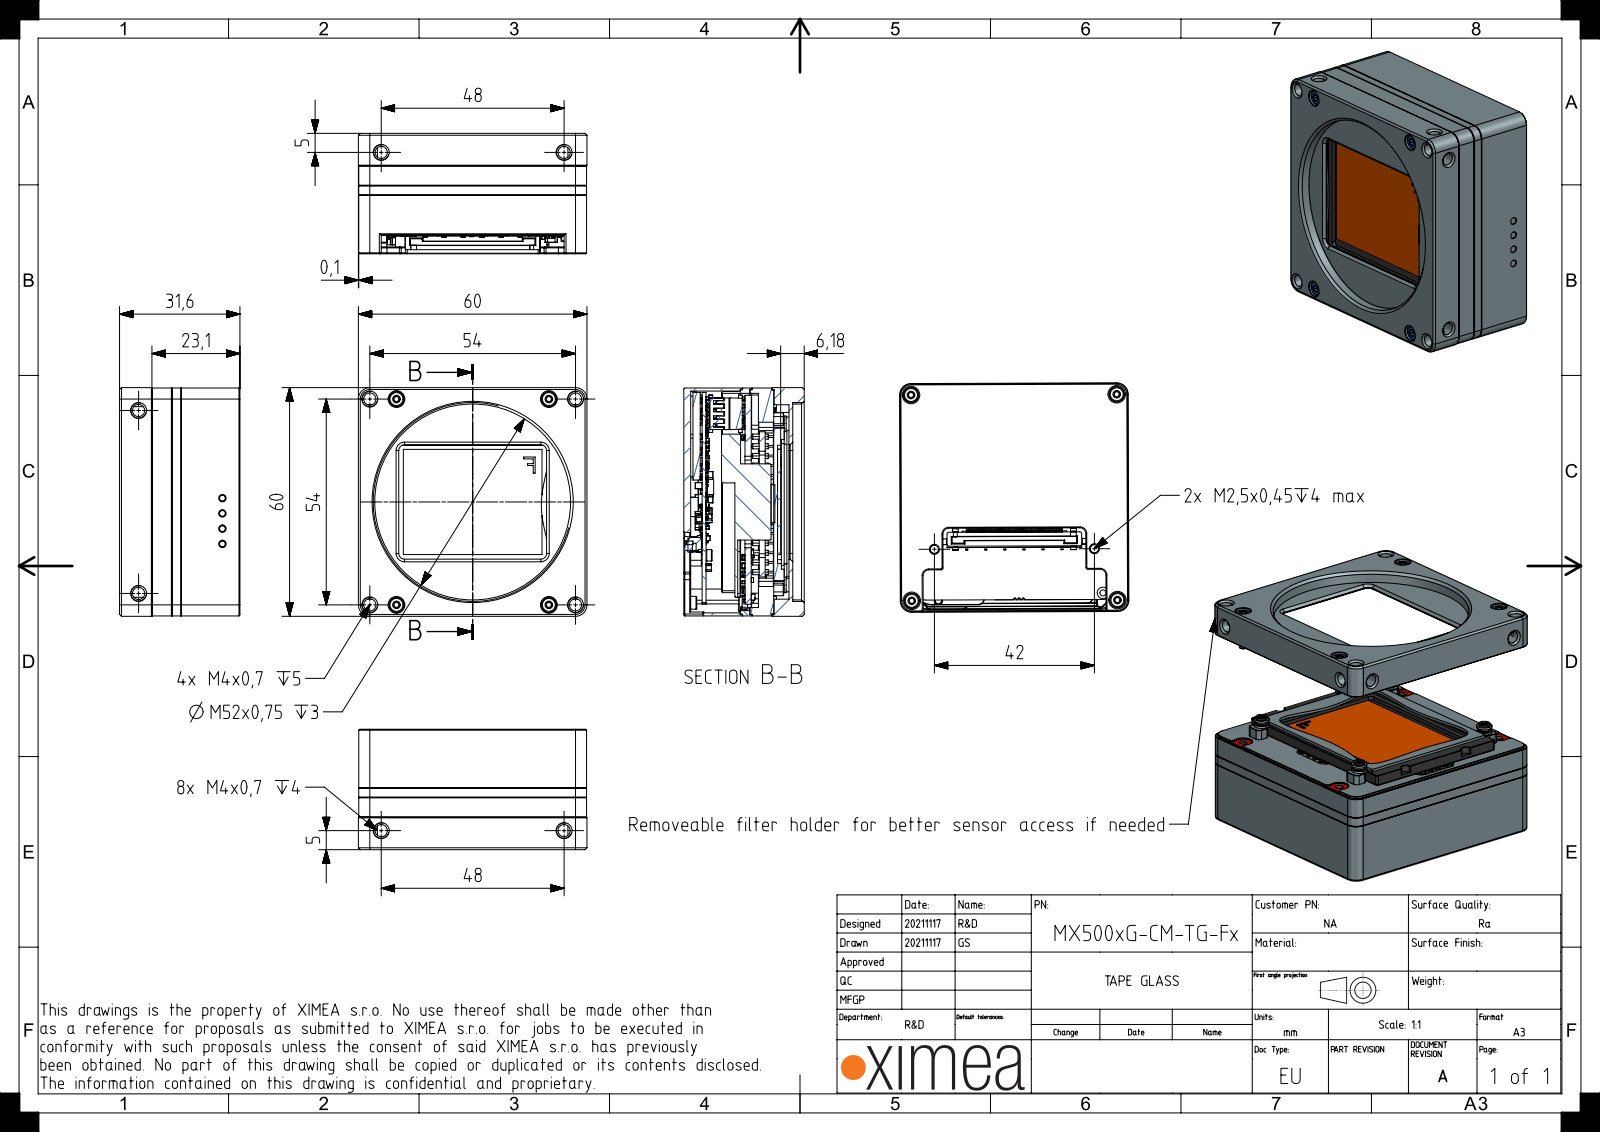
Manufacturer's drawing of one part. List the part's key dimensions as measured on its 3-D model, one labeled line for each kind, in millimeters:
Part name (STEP PRODUCT): MECH-LIGHTPIPE-1.63X4.14; MECH-MX-X4L-REAR; MX-X4L-MAIN-FL-PCA-6A-LW; SROB-M1.6X4-TX-STNLS (+8 more)
STEP written by: SIEMENS PLM Software NX 1907 (AUTOMOTIVE_DESIGN)
Units: millimetres
Bodies: 201 solids, 21802 faces (17789 planar, 3381 cylindrical, 632 other)
Overall size (bounding box): 60 × 60 × 31.6
Volume: 52 650 mm³ · Surface area: 71 680 mm²
Round holes (diameter × count): ⌀1.3 ×141, ⌀1.6 ×21, ⌀2.1 ×17, ⌀1.3 ×10, ⌀2 ×8, ⌀3.2 ×8, ⌀4.1 ×8, ⌀1 ×5, ⌀1.5 ×4, ⌀4.7 ×4, ⌀4.8 ×4, ⌀1.4 ×3
Round bosses / shafts (diameter × count): ⌀0.5 ×140, ⌀3 ×12, ⌀3.8 ×8, ⌀1.9 ×7, ⌀1.8 ×5, ⌀4 ×4, ⌀1.6 ×4, ⌀0.8 ×4
Partial cylindrical surfaces — rounded edges, fillets, slot ends (radius × count): R0.1 ×81, R0.3 ×60, R1 ×59, R0.5 ×51, R3 ×42, R0.3 ×38, R0.1 ×30, R0.2 ×30
Main face-to-face distances: 3, 1, 22.8, 4, 17.7, 18.8, 1, 17.8, 0.9, 59
Hole centre spacings: 2.5, 3.6, 5.1, 5.7, 7.6, 8, 10.2, 10.5
